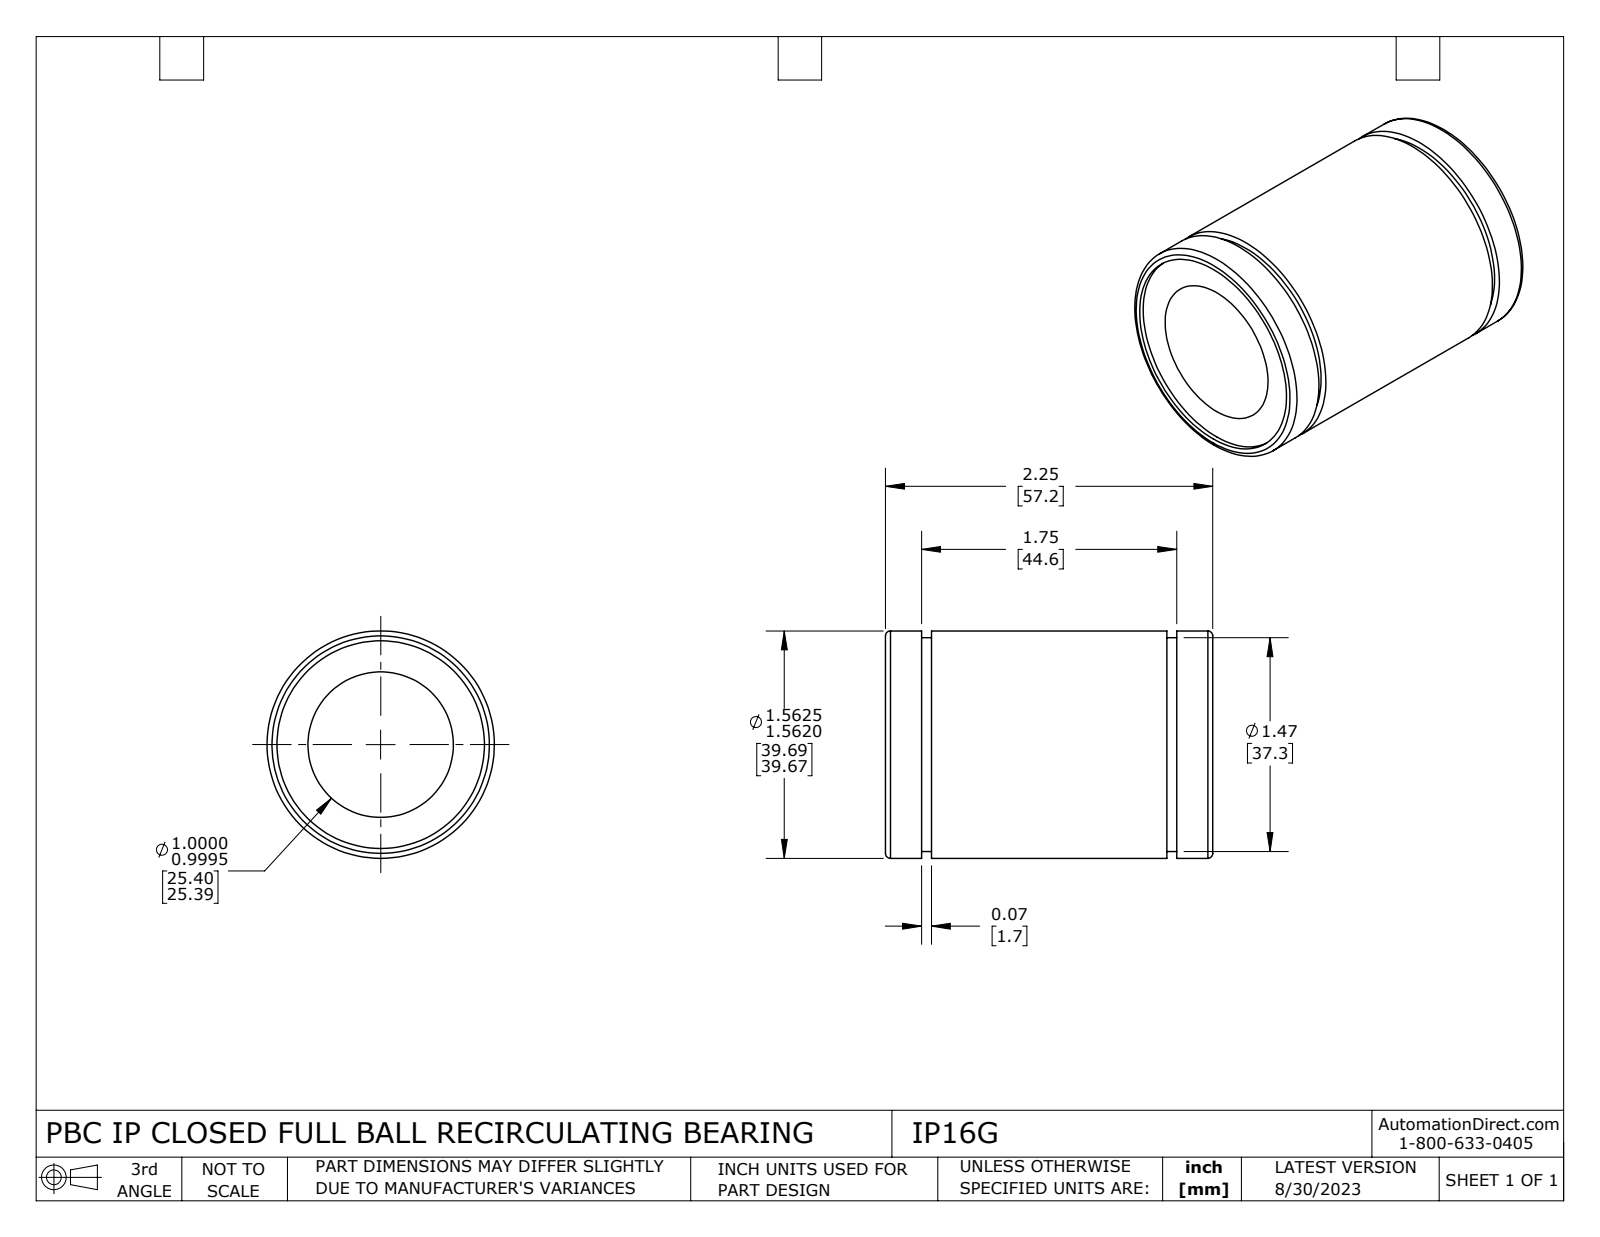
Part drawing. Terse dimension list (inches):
name: IP16G
written by: SolidWorks 2021 (CONFIG_CONTROL_DESIGN)
unit: in
bodies: 1 solid, 28 faces (8 planar, 16 cylindrical, 4 other)
size: 2.25 × 1.563 × 1.563
volume: 2.459 in³; area: 21.18 in²
holes: 1× ⌀1, 1× ⌀1.427
bosses: 1× ⌀1.563, 1× ⌀1.469
face distances: 2.182, 0.281, 1.9, 0.214, 1.968, 0.068, 1.687, 0.034, 0.248, 0.315
